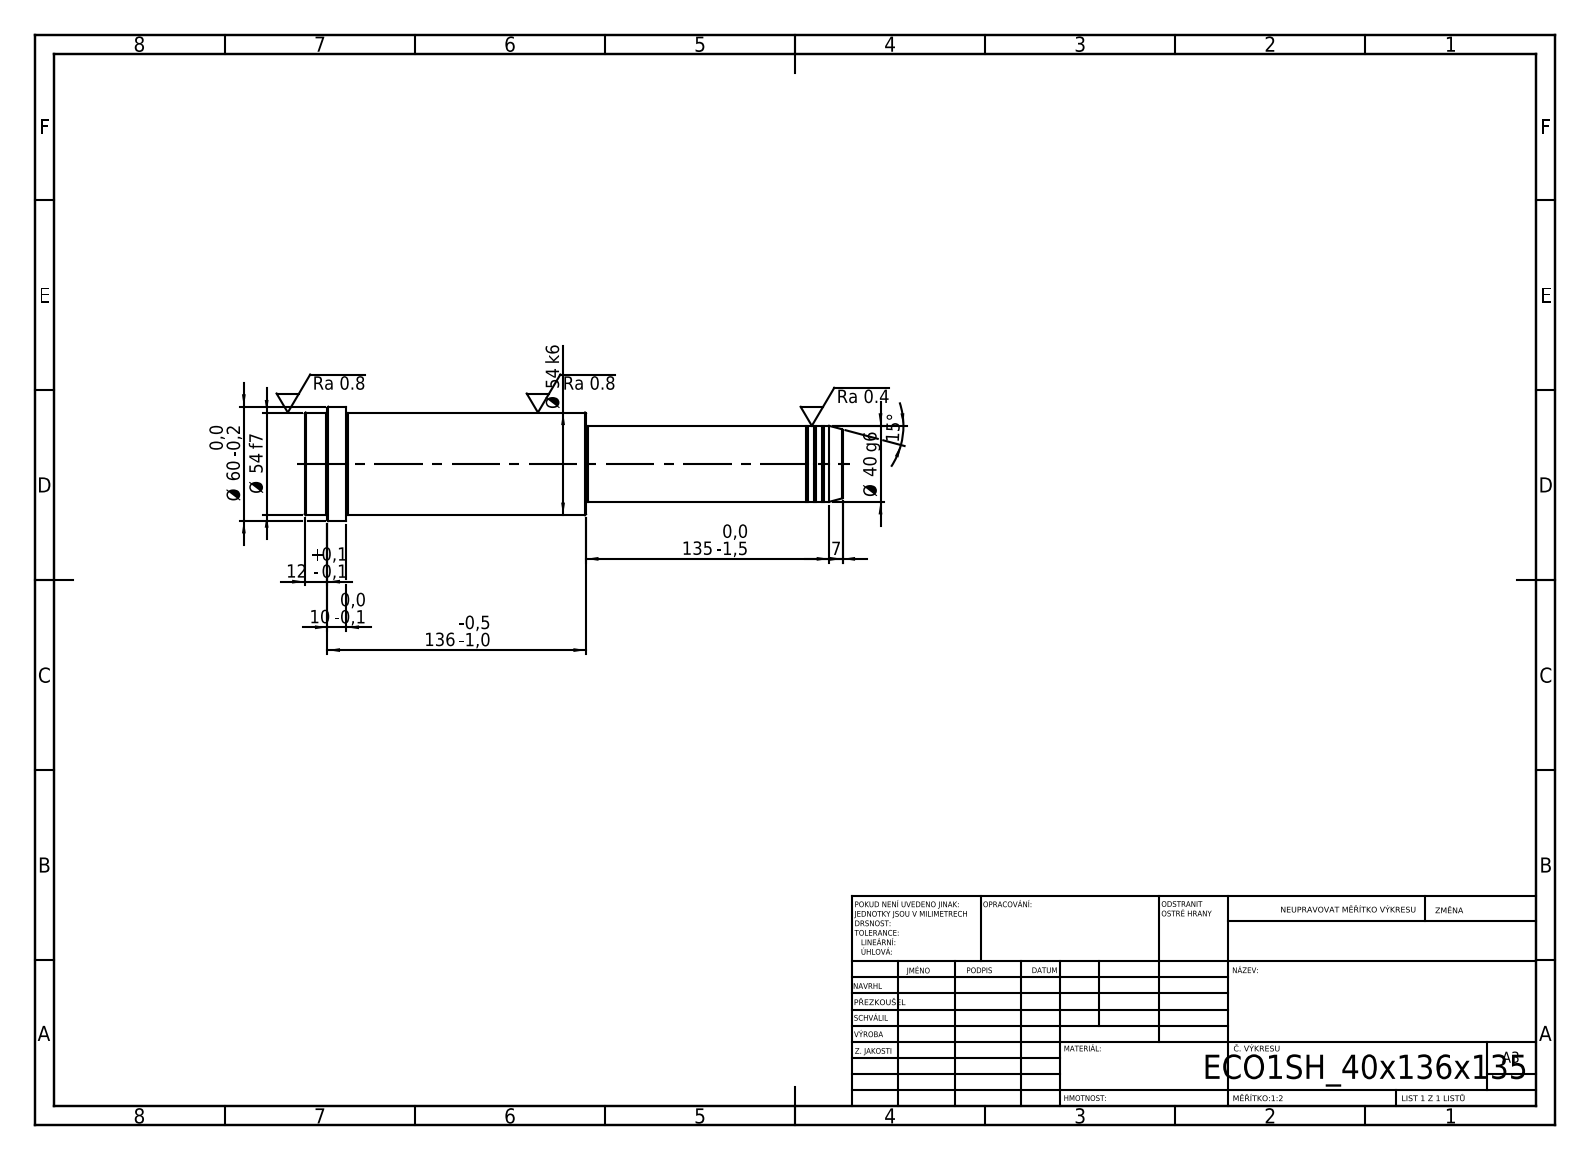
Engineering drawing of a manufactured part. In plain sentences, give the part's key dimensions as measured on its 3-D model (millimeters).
Its 3-D file was written by "SolidWorks 2019 (CONFIG_CONTROL_DESIGN)". It is 1 solid with 52 faces: 6 planar, 16 cylindrical and 30 other. Overall it measures 283 by 60 by 60 millimeters. Its volume is 512 762 cubic millimeters and its surface area 48 025 square millimeters. Round bosses or shafts: 1 of diameter 60, 1 of diameter 54, 1 of diameter 40, 1 of diameter 39. The main face-to-face distances are 148, 135, 283, 261, 126, 22, 271, 136, 10, 12.
